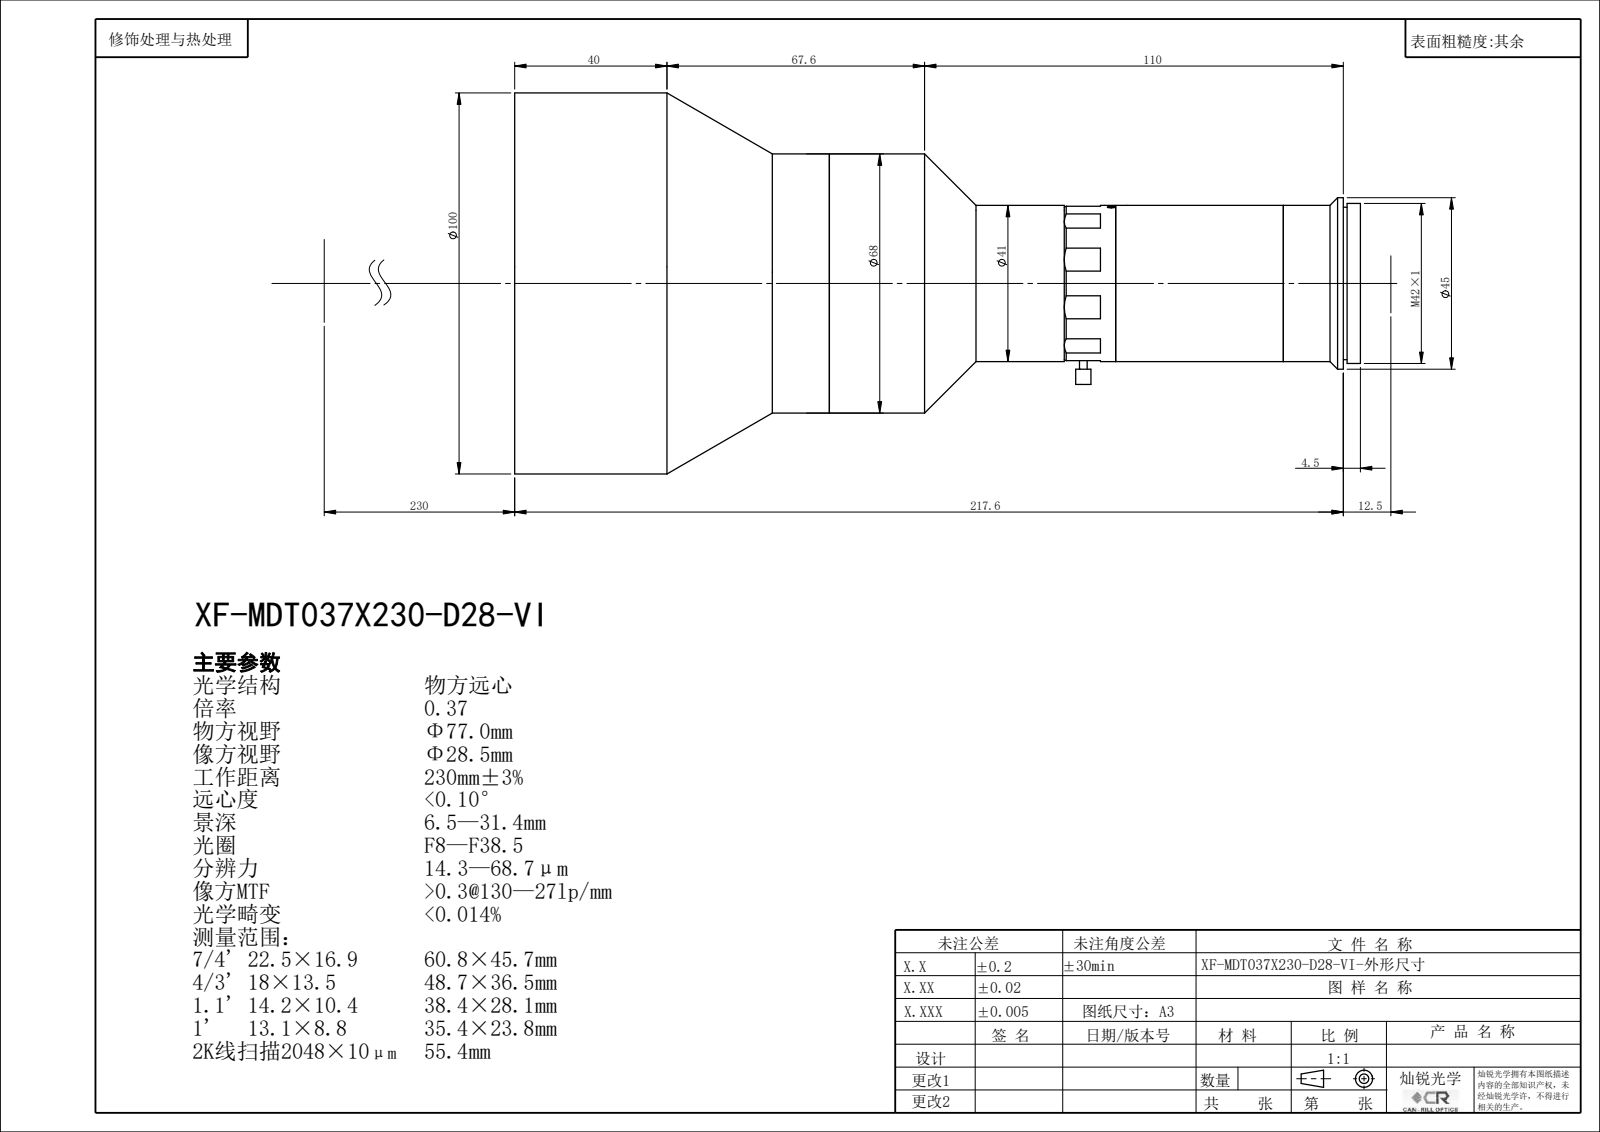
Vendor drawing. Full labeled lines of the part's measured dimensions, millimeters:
Part name (STEP PRODUCT): XF-MDT037X230-D28-VI
STEP written by: SolidWorks 2018 (CONFIG_CONTROL_DESIGN)
Units: millimetres
Bodies: 0 solids, 99 faces (30 planar, 47 cylindrical, 22 other)
Overall size (bounding box): 222.1 × 100 × 100
Round holes (diameter × count): ⌀32 ×1, ⌀90 ×1, ⌀94 ×1
Round bosses / shafts (diameter × count): ⌀100 ×1, ⌀68 ×1, ⌀45 ×1, ⌀42 ×1, ⌀41 ×1, ⌀40 ×1, ⌀4 ×1, ⌀2 ×1
Partial cylindrical surfaces — rounded edges, fillets, slot ends (radius × count): R20 ×10, R20.4 ×1
Main face-to-face distances: 82.65, 9.8, 72.85, 144.33, 134.53, 61.68, 222.1, 212.3, 139.45, 77.77
